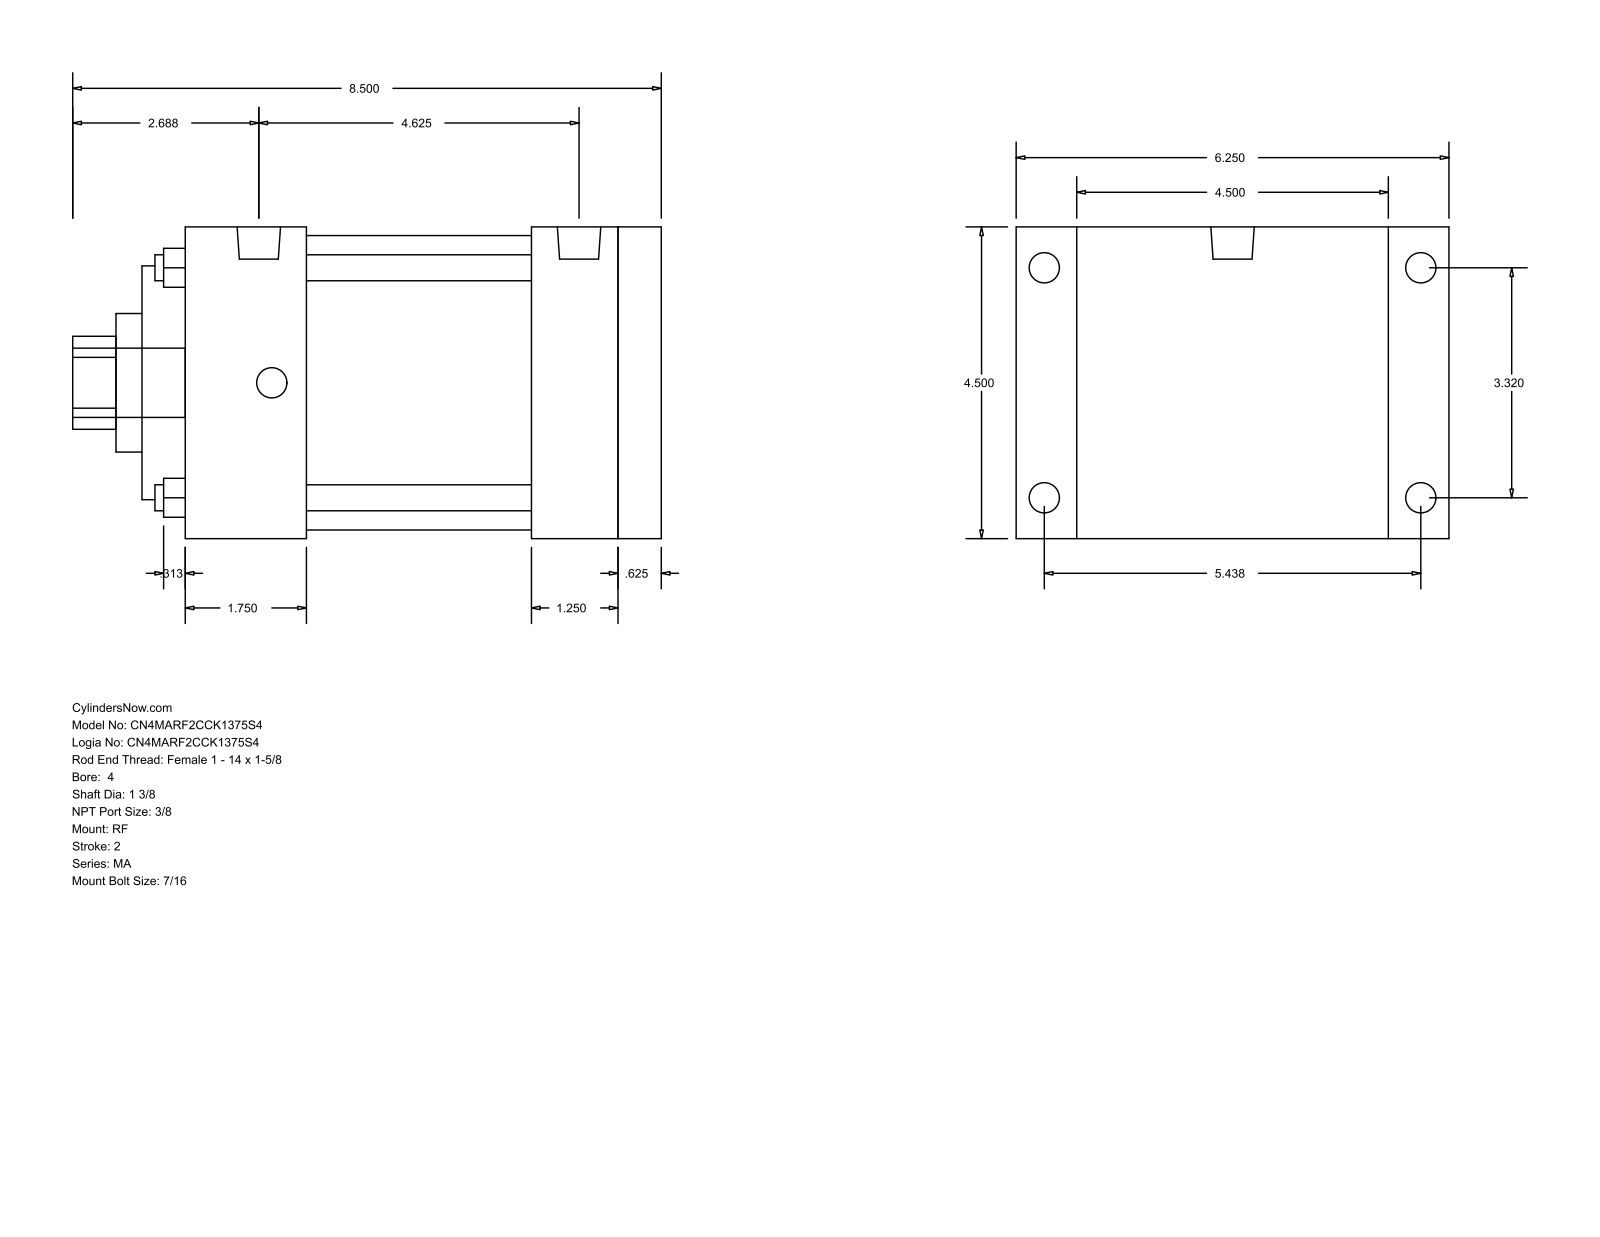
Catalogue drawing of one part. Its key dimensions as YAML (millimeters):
part_name: "MA_RF__0400_1.375"
step_written_by: "GSSL Pune (CONFIG_CONTROL_DESIGN)"
units: millimeters
bodies: {solids: 0, faces: 94, planar: 65, cylindrical: 29, other: 0}
overall_size: [215.9, 158.75, 114.3]
round_holes:
  - {diameter: 9.53, count: 4}
  - {diameter: 34.92, count: 1}
  - {diameter: 50.8, count: 1}
  - {diameter: 85.72, count: 1}
  - {diameter: 107.95, count: 1}
round_bosses_or_shafts:
  - {diameter: 11.11, count: 8}
  - {diameter: 15.93, count: 2}
  - {diameter: 25.4, count: 1}
partial_cylinders:
  - {radius: 17.06, count: 1}
face_to_face_distances: [114.3, 174.63, 15.87, 158.76, 190.5, 22.23, 136.53, 142.88, 127.01, 31.75]
hole_center_spacings: [59.62, 84.32, 119.25]
